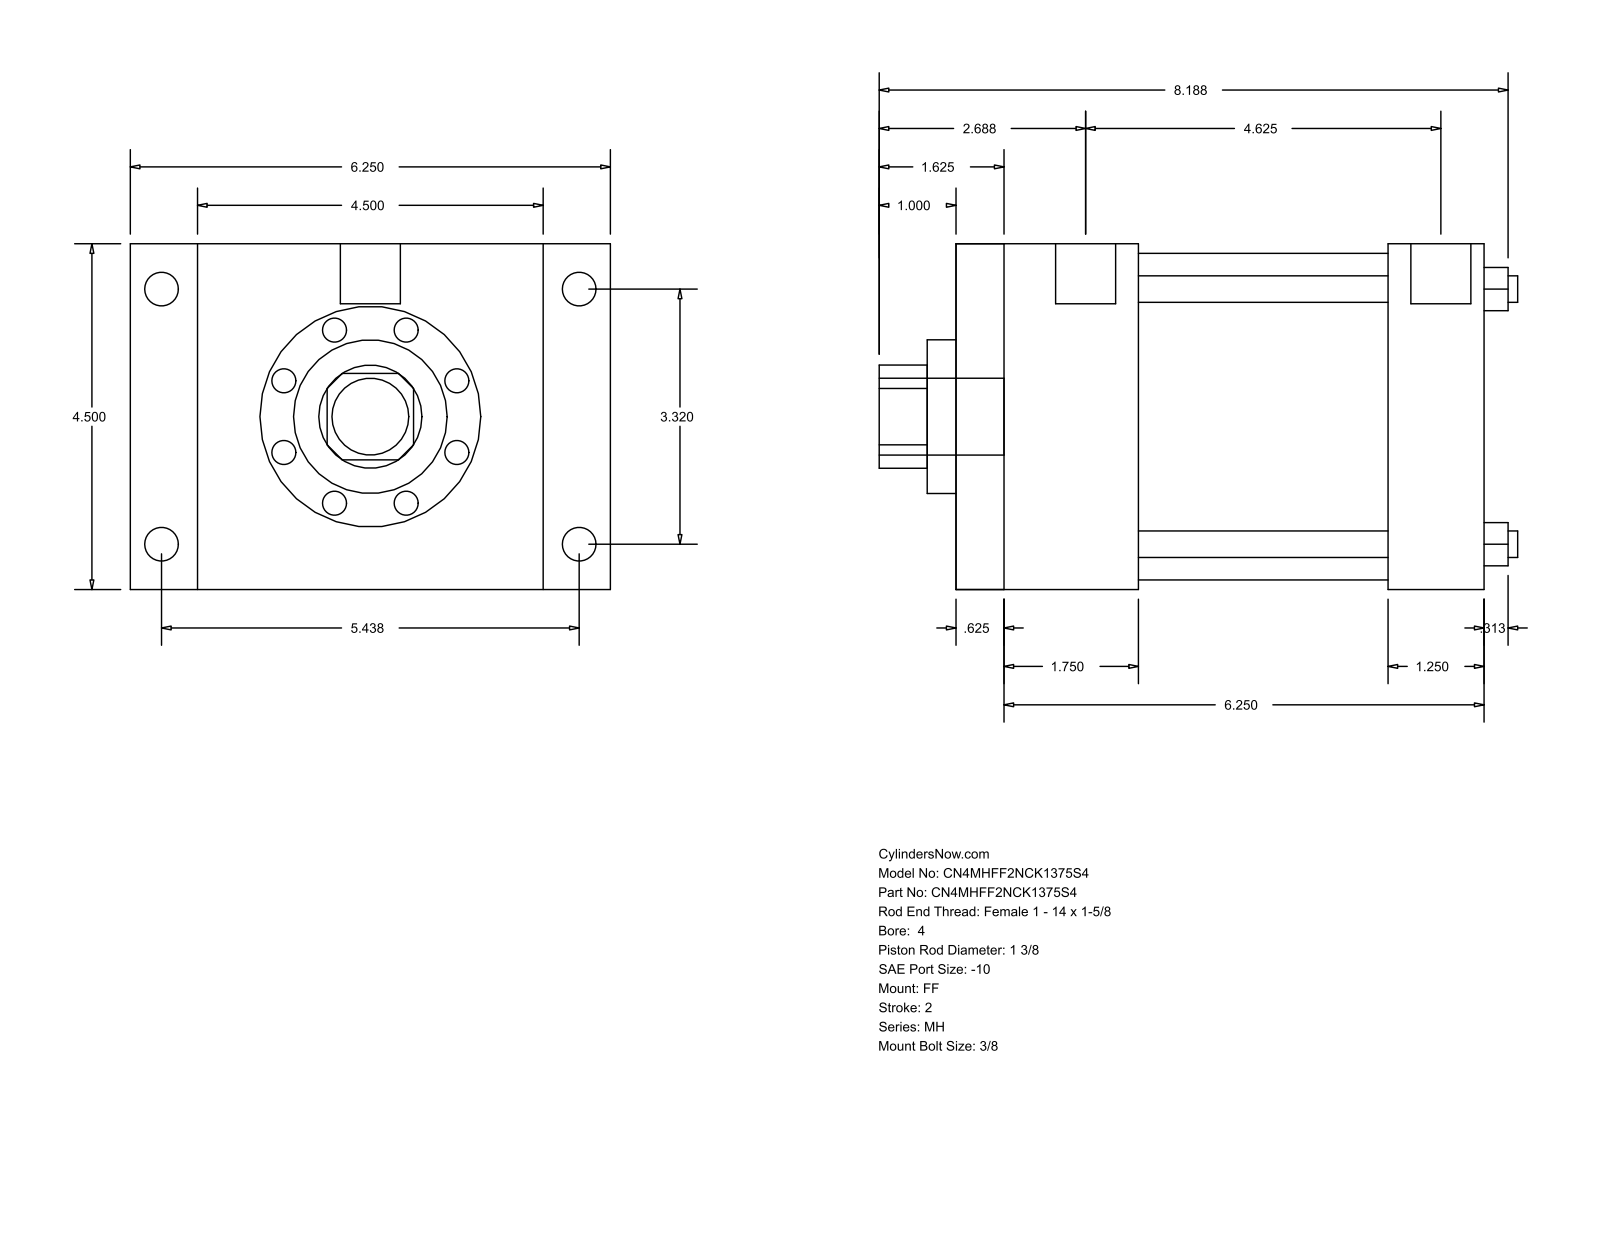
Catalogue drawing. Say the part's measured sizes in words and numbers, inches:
The part is named "MH_FF__0400_1.375". Its 3-D file was written by "GSSL Pune (CONFIG_CONTROL_DESIGN)". It is 0 solids with 92 faces: 64 planar, 28 cylindrical and 0 other. Overall it measures 8.313 by 6.25 by 4.5 inches. Round holes: 4 of diameter 0.345, 1 of diameter 1.375, 1 of diameter 2, 1 of diameter 4.25. Round bosses or shafts: 4 of diameter 0.438, 4 of diameter 0.344, 2 of diameter 0.781, 1 of diameter 1. Partial cylindrical surfaces (rounded edges, fillets, slot ends): 1 of radius 0.672. The main face-to-face distances are 4.5, 6.875, 6.25, 0.625, 2.375, 1.75, 4.5, 5.625, 5, 3.25. The hole center spacings are 2.347, 3.32, 4.695.
